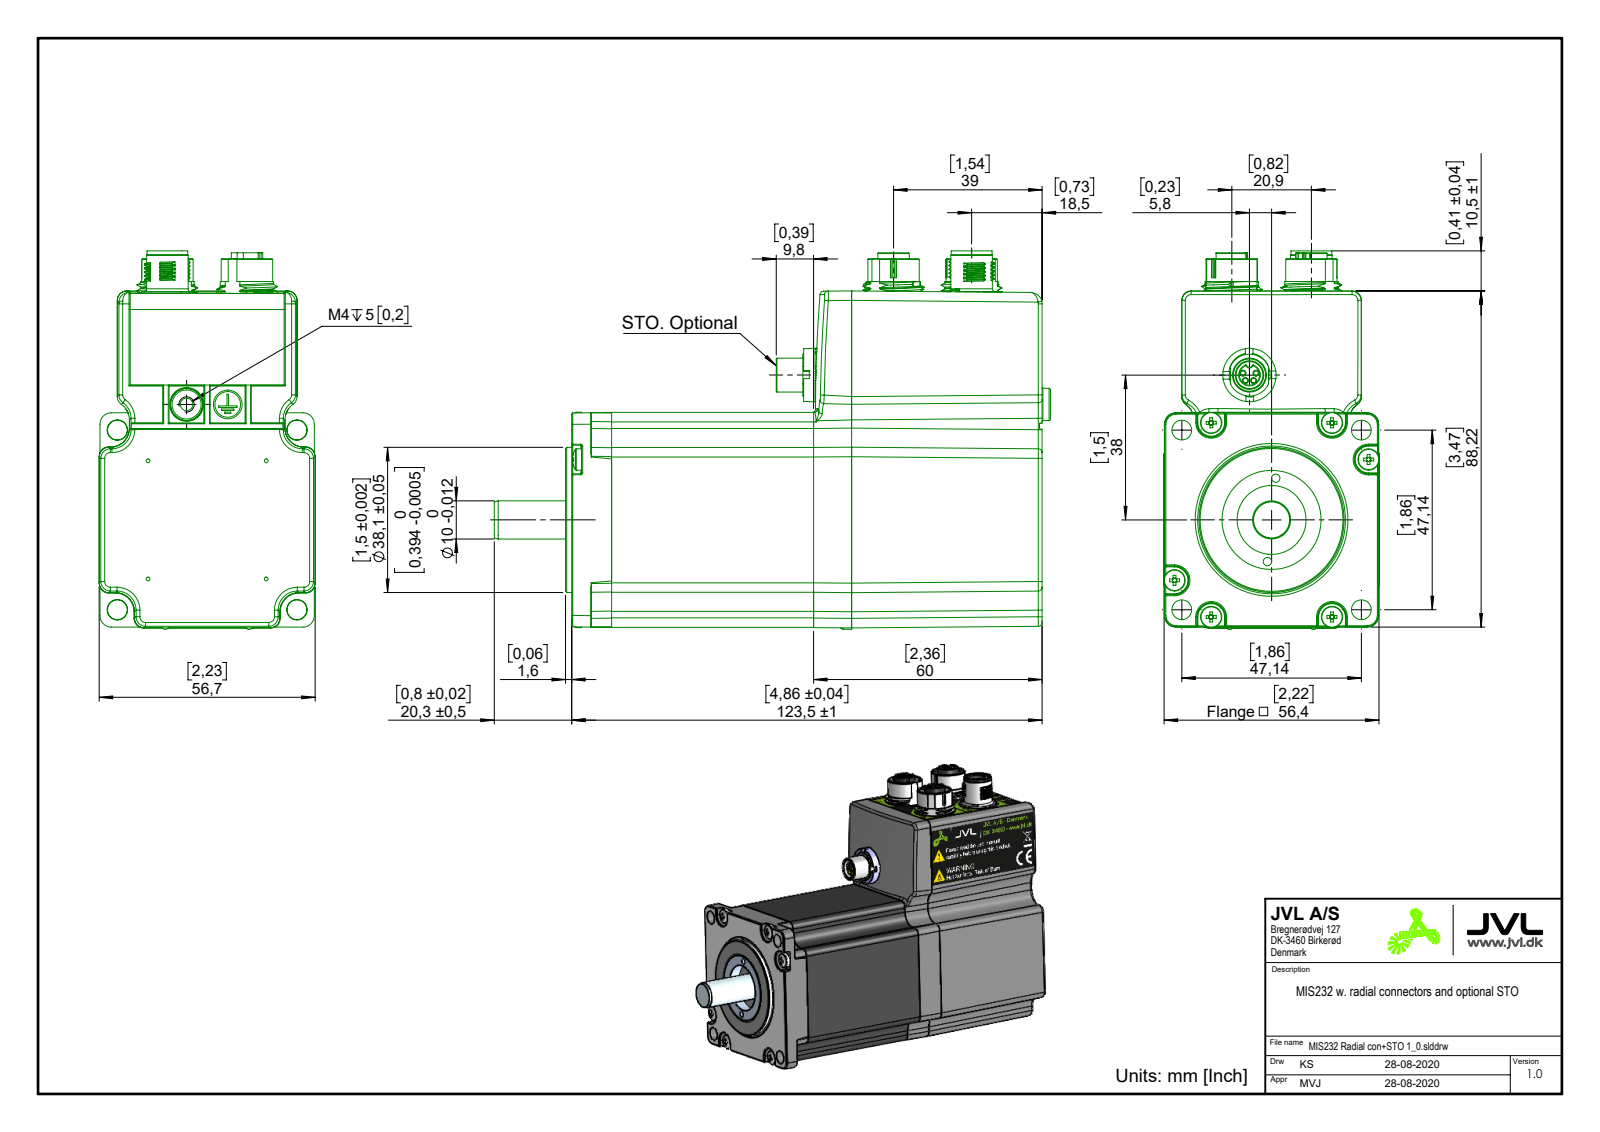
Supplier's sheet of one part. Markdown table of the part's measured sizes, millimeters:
| quantity | value |
| --- | --- |
| part name | MIS23X |
| STEP written by | SolidWorks 2018 (AUTOMOTIVE_DESIGN) |
| units | millimeters |
| bodies | 2 solids, 2109 faces (897 planar, 530 cylindrical, 682 other) |
| overall size | 146 × 99.33 × 56.67 |
| volume | 445 139 mm³ |
| surface area | 48 874 mm² |
| round holes (diameter × count) | 1 × 31, 1.2 × 4, 12.2 × 3, 15.5 × 3, 2.2 × 2, 2.5 × 2, 11.13 × 2, 3.3 × 1, 6.76 × 1, 7.1 × 1, 8.3 × 1, 10.9 × 1 |
| round bosses / shafts (diameter × count) | 5.6 × 6, 3 × 6, 1 × 5, 1.6 × 4, 0.8 × 4, 13.5 × 3, 38.1 × 1, 14 × 1 |
| partial cylindrical surfaces (radius × count) | 0.2 × 66, 2.5 × 29, 0.1 × 20, 5 × 18, 0.3 × 16, 1 × 15, 0.8 × 13, 2.3 × 8 |
| main face-to-face distances | 56.4, 4.75, 123.5, 51.92, 0.5, 123, 9.2, 47.2, 56.67, 125.1 |
| hole center spacings | 3.54, 1.63, 2.5, 3.25, 1.85, 4.94, 1.64, 2.83 |
